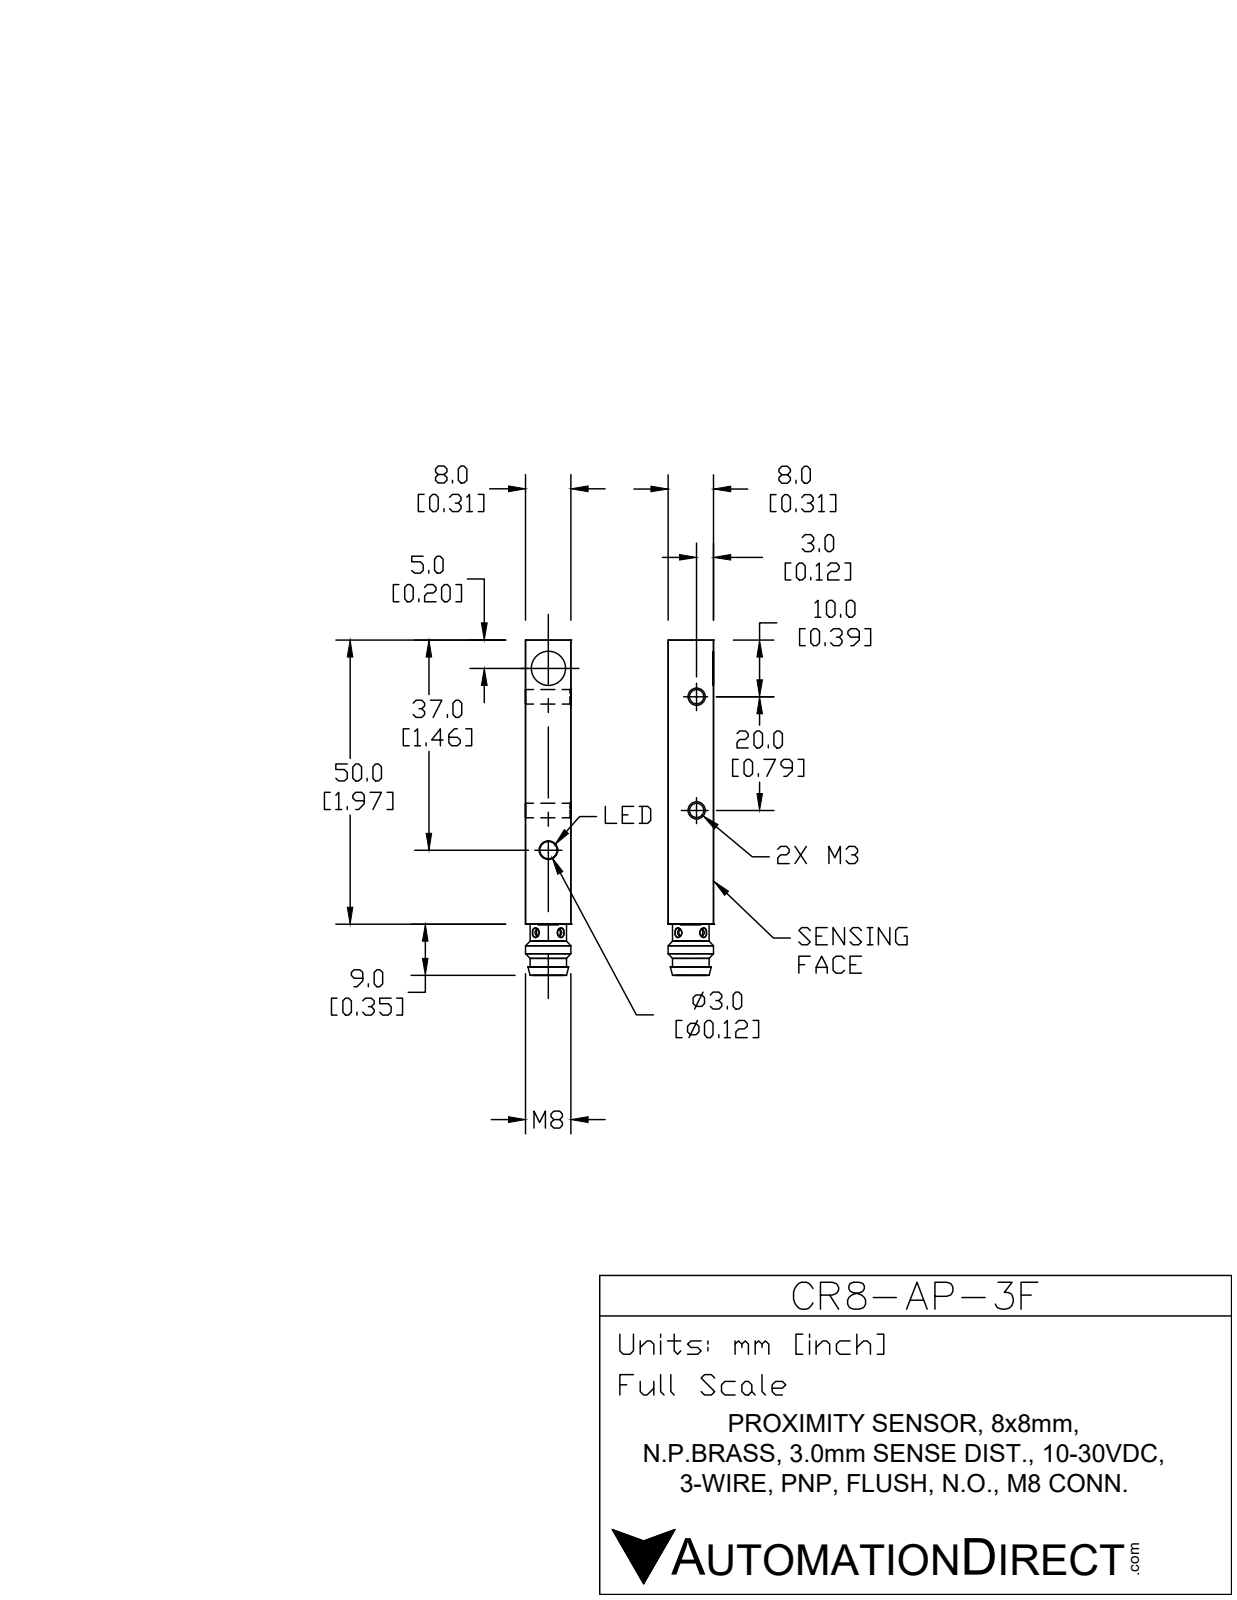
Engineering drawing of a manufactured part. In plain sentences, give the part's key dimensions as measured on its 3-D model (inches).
The part is named "CR8-AP-3F". Its 3-D file was written by "SolidWorks 2017 (AUTOMOTIVE_DESIGN)". It is 2 solids with 63 faces: 23 planar, 23 cylindrical and 17 other. Overall it measures 2.323 by 0.315 by 0.315 inches. Its volume is 0.219 cubic inches and its surface area 6.236 square inches. Round holes: 2 of diameter 0.098, 1 of diameter 0.228, 1 of diameter 0.24, 1 of diameter 0.256. Round bosses or shafts: 2 of diameter 0.039, 1 of diameter 0.315, 1 of diameter 0.272, 1 of diameter 0.268, 1 of diameter 0.256, 1 of diameter 0.256, 1 of diameter 0.04. Partial cylindrical surfaces (rounded edges, fillets, slot ends): 4 of radius 0.039, 2 of radius 0.132. The main face-to-face distances are 0.026, 0.289, 0.315, 0.264, 0.059, 0.256, 0.098, 0.039, 0.217, 0.185. The hole center spacings are 0.787.
